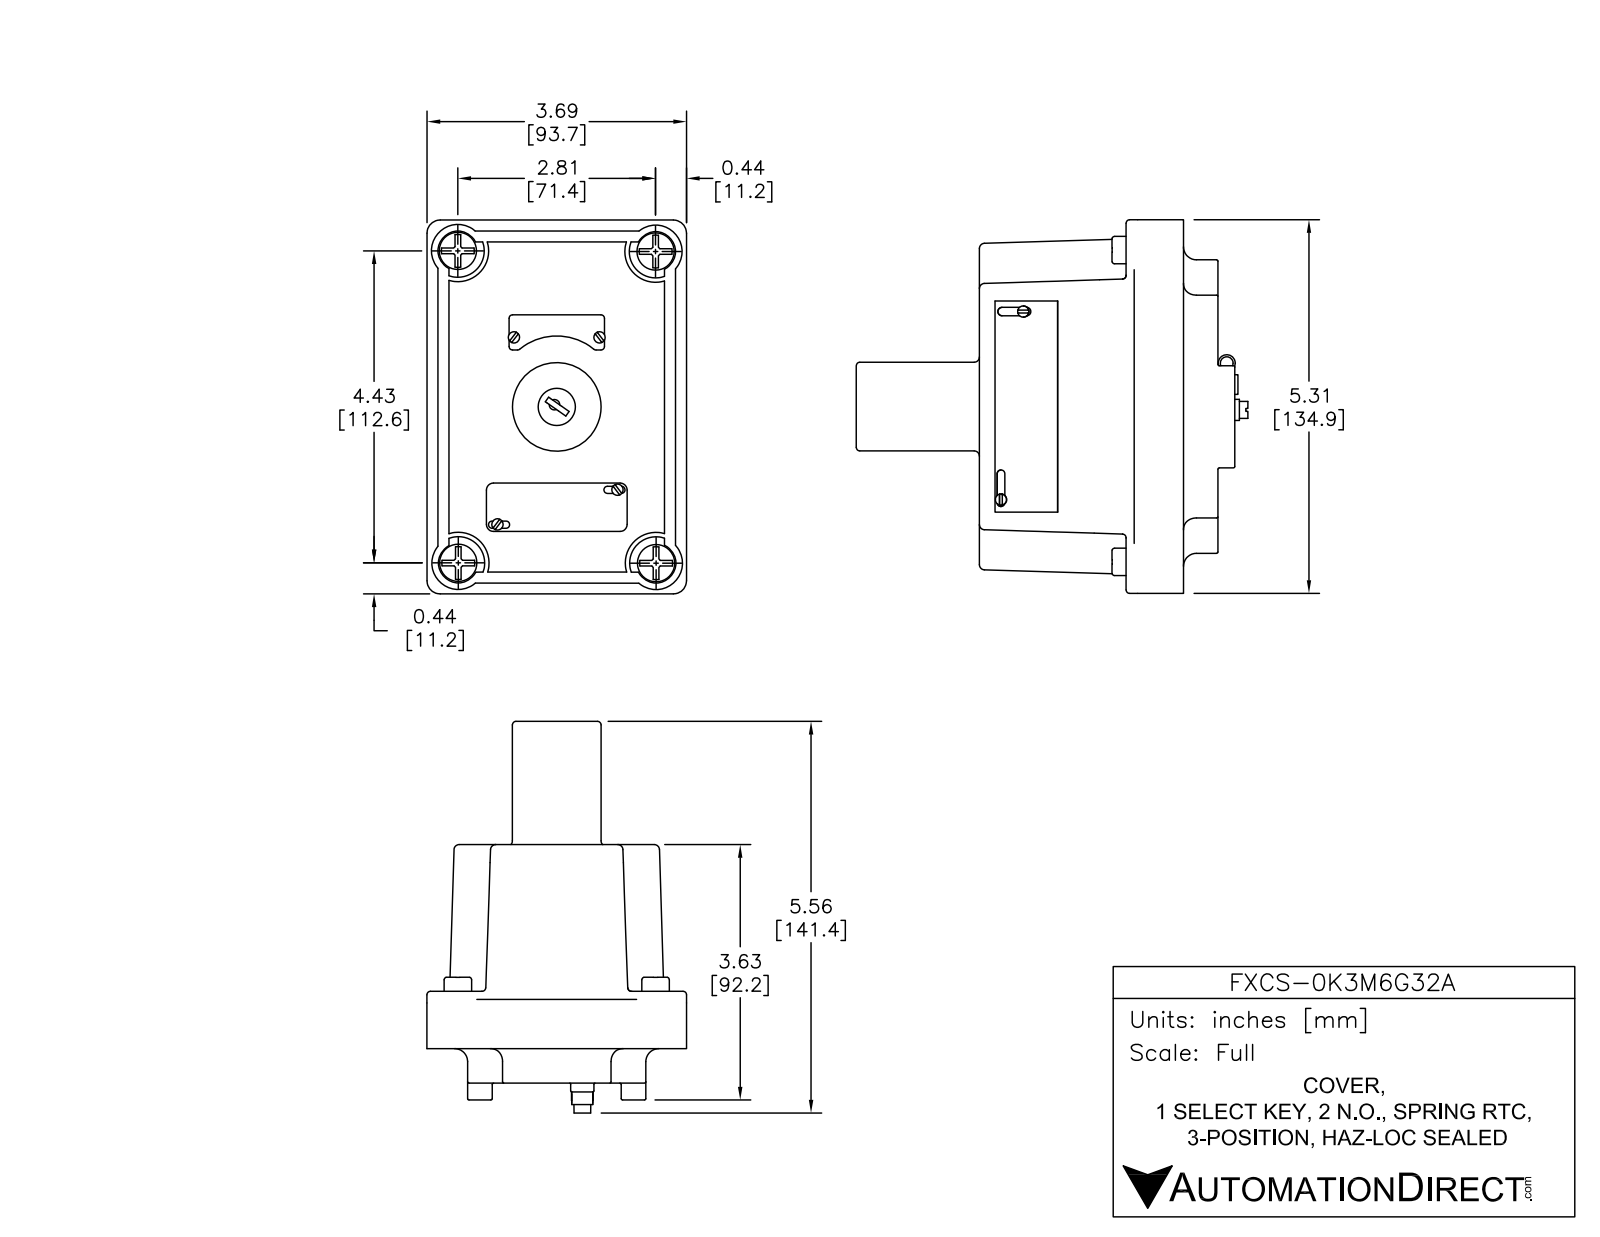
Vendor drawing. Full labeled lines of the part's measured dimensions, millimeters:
Part name (STEP PRODUCT): FXCS-0K3M6G32A
STEP written by: SolidWorks 2015 (AUTOMOTIVE_DESIGN)
Units: millimetres
Bodies: 2 solids, 699 faces (303 planar, 157 cylindrical, 239 other)
Overall size (bounding box): 141.4 × 134.9 × 93.7
Volume: 820 500 mm³ · Surface area: 63 940 mm²
Round holes (diameter × count): ⌀4.1 ×8, ⌀5 ×1, ⌀13.4 ×1
Round bosses / shafts (diameter × count): ⌀4.1 ×8, ⌀9.9 ×4, ⌀32 ×1, ⌀8.4 ×1, ⌀7.6 ×1, ⌀6.1 ×1
Partial cylindrical surfaces — rounded edges, fillets, slot ends (radius × count): R1.3 ×24, R0.5 ×22, R1.3 ×4, R1.4 ×4, R1.5 ×4, R1.9 ×4, R2.5 ×4, R4.7 ×4
Main face-to-face distances: 86.1, 12.4, 73.7, 0.5, 93.7, 14.7, 79, 30.2, 17.8, 55.9
Hole centre spacings: 6.4, 55.8, 12.7, 55.4, 56.9, 19.1, 27.7, 28.3
